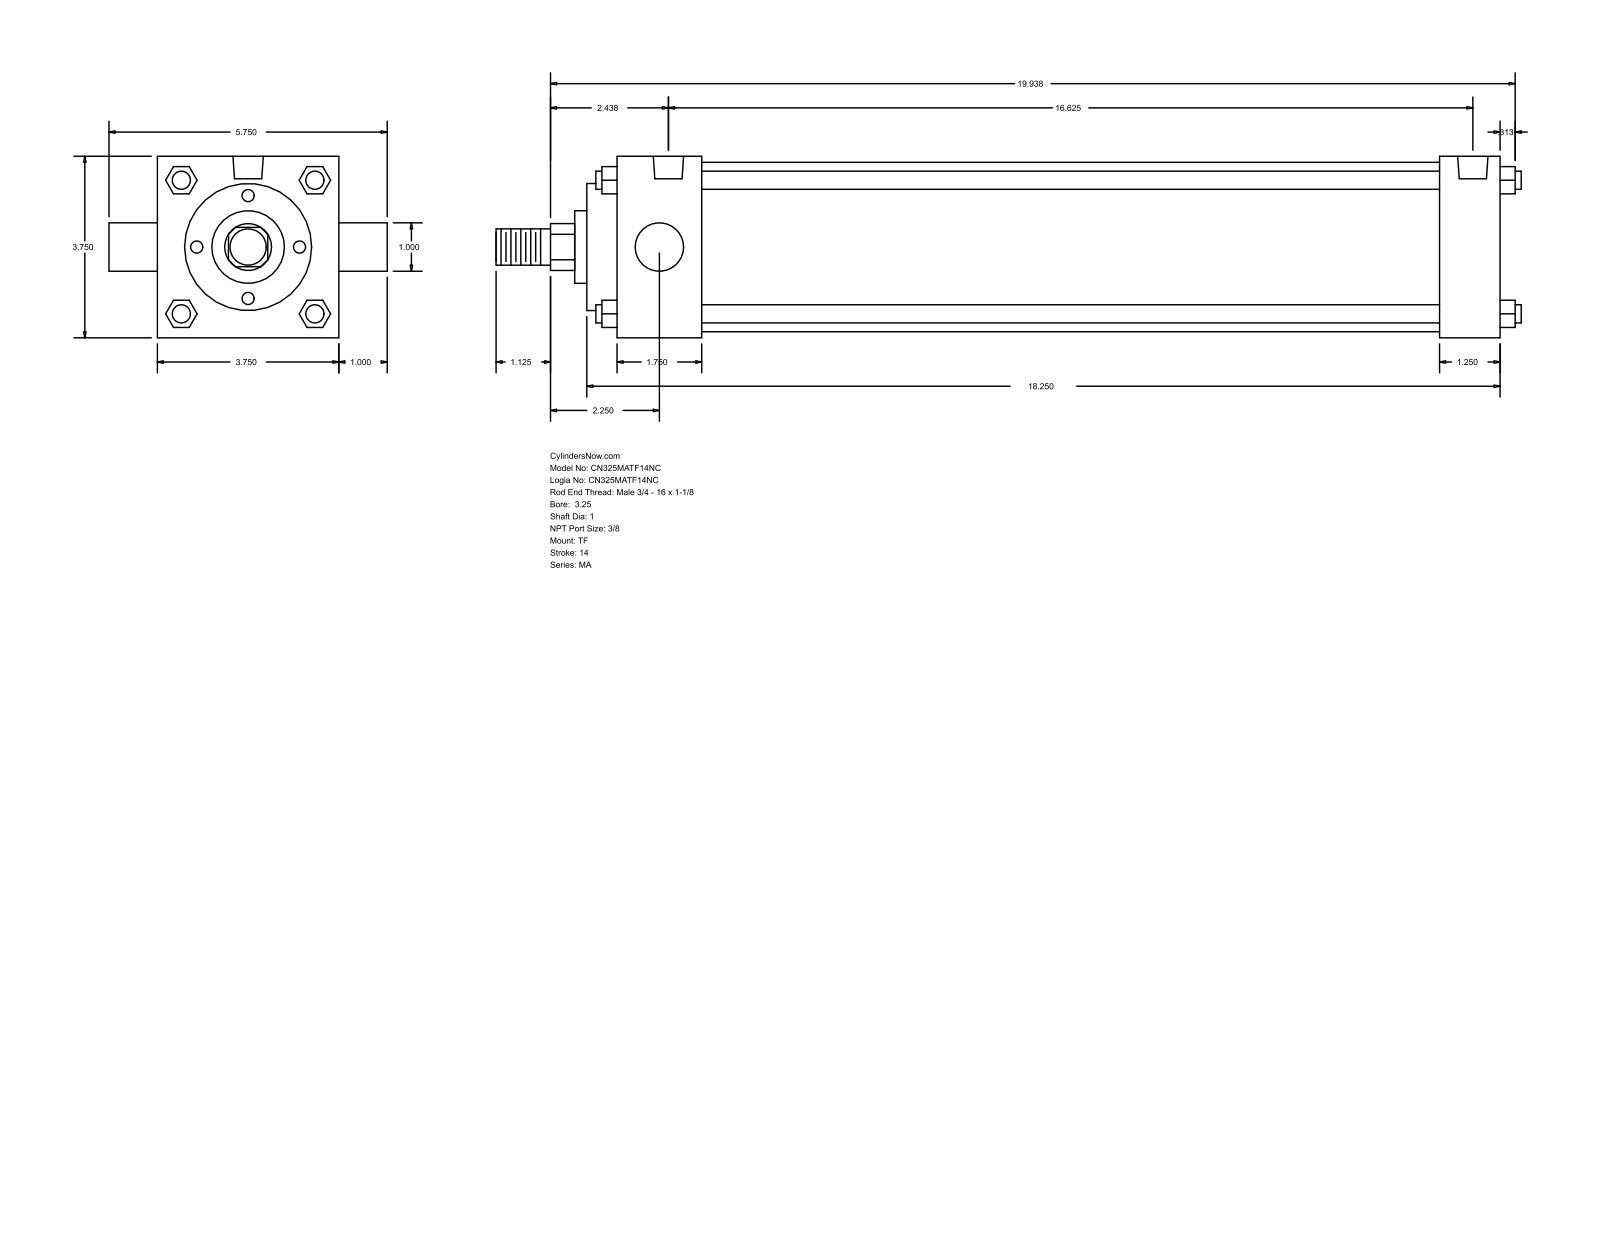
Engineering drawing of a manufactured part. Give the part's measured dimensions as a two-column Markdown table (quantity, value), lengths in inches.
| quantity | value |
| --- | --- |
| part name | MA_TF__0325_1 |
| STEP written by | GSSL Pune (CONFIG_CONTROL_DESIGN) |
| units | inches |
| bodies | 0 solids, 122 faces (93 planar, 29 cylindrical, 0 other) |
| overall size | 21.187 × 5.75 × 3.75 |
| round holes (diameter × count) | 0.437 × 3, 0.627 × 2 |
| round bosses / shafts (diameter × count) | 0.375 × 4, 1 × 2, 3.5 × 1, 2.625 × 1, 1.5 × 1, 0.75 × 1 |
| partial cylindrical surfaces (radius × count) | 0.484 × 1 |
| main face-to-face distances | 3.75, 18.25, 1.75, 17, 15.25, 16.5, 1.25, 0.625, 2.375, 17.625 |
| hole center spacings | 0.187, 16.438, 16.25, 16.625 |
